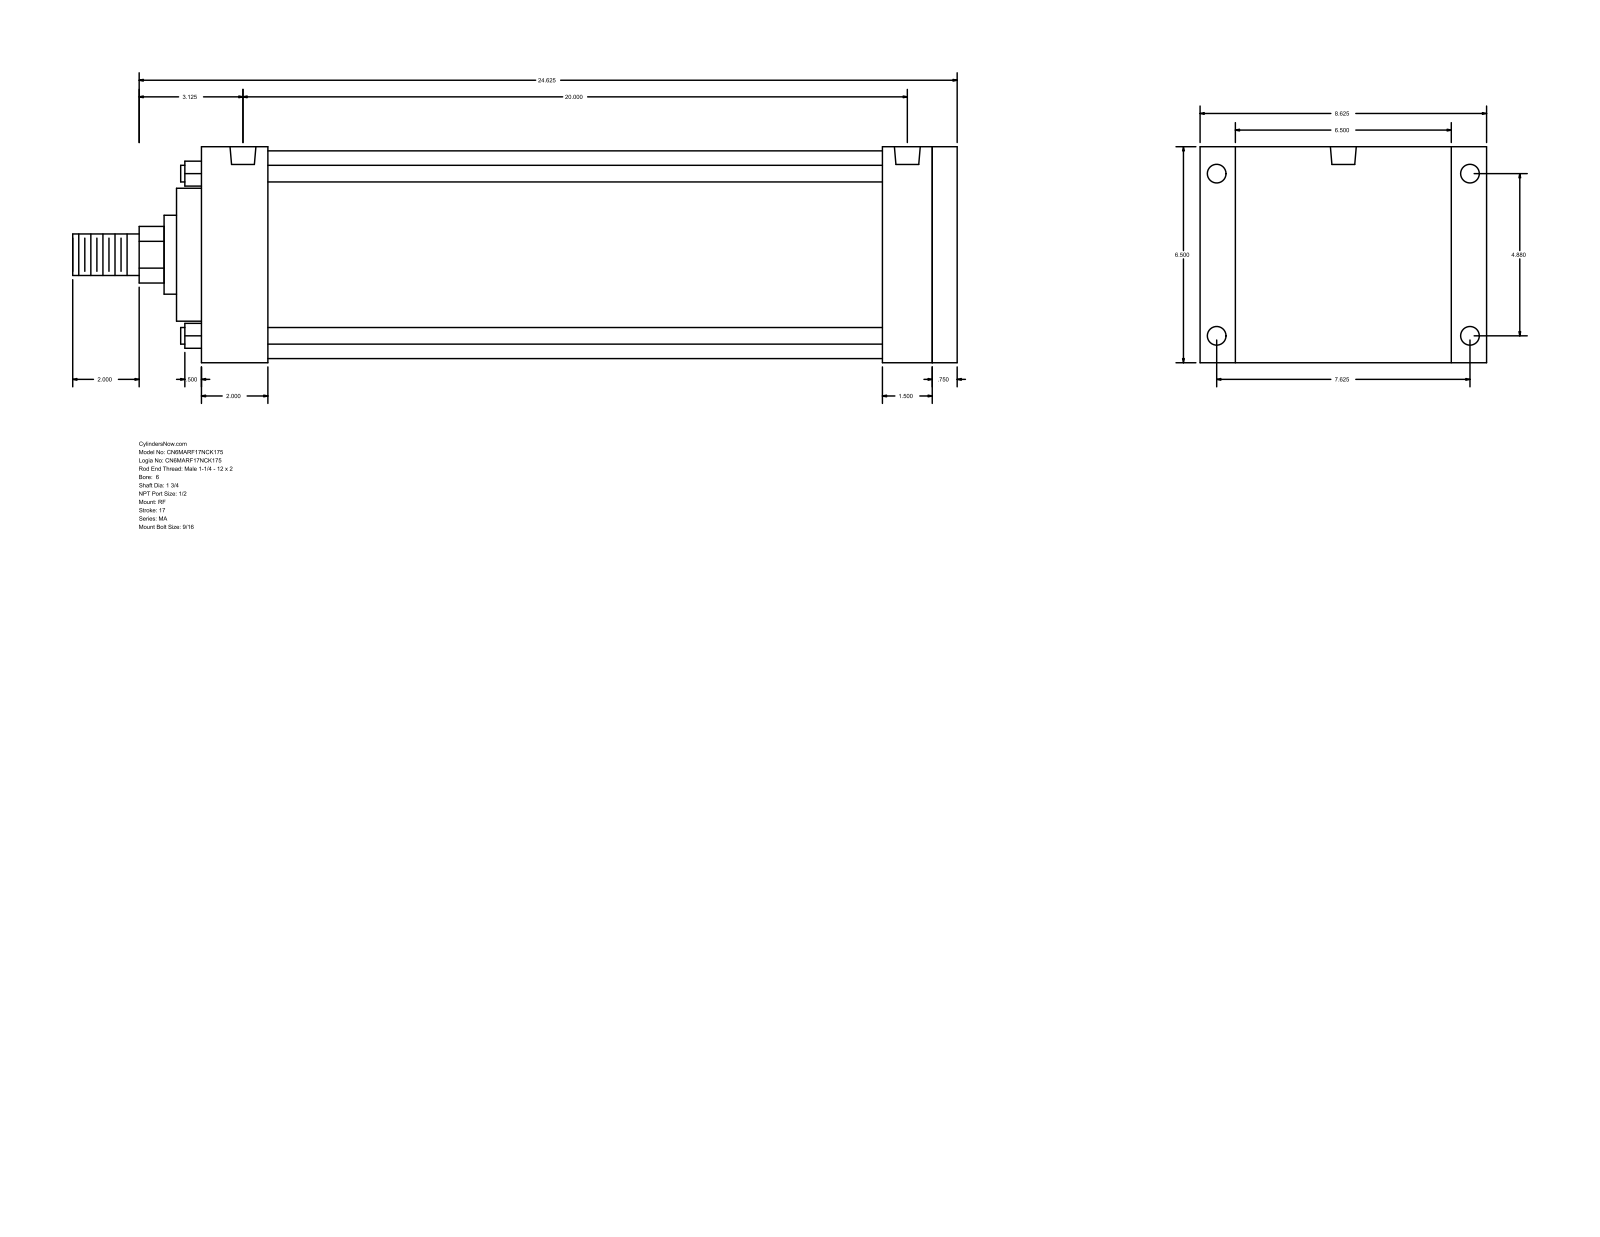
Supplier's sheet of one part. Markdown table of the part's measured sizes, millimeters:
| quantity | value |
| --- | --- |
| part name | MA_RF__0600_1.75 |
| STEP written by | GSSL Pune (CONFIG_CONTROL_DESIGN) |
| units | millimeters |
| bodies | 0 solids, 94 faces (65 planar, 29 cylindrical, 0 other) |
| overall size | 676.27 × 219.07 × 165.1 |
| round holes (diameter × count) | 14.29 × 4, 17.46 × 4, 19.77 × 2 |
| round bosses / shafts (diameter × count) | 12.7 × 4, 158.75 × 1, 101.6 × 1, 60.33 × 1, 44.45 × 1, 31.75 × 1 |
| partial cylindrical surfaces (radius × count) | 21.63 × 1 |
| main face-to-face distances | 165.1, 577.86, 558.8, 19.06, 50.8, 19.05, 508, 527.06, 520.71, 469.91 |
| hole center spacings | 123.96, 193.68, 229.95, 508 |
